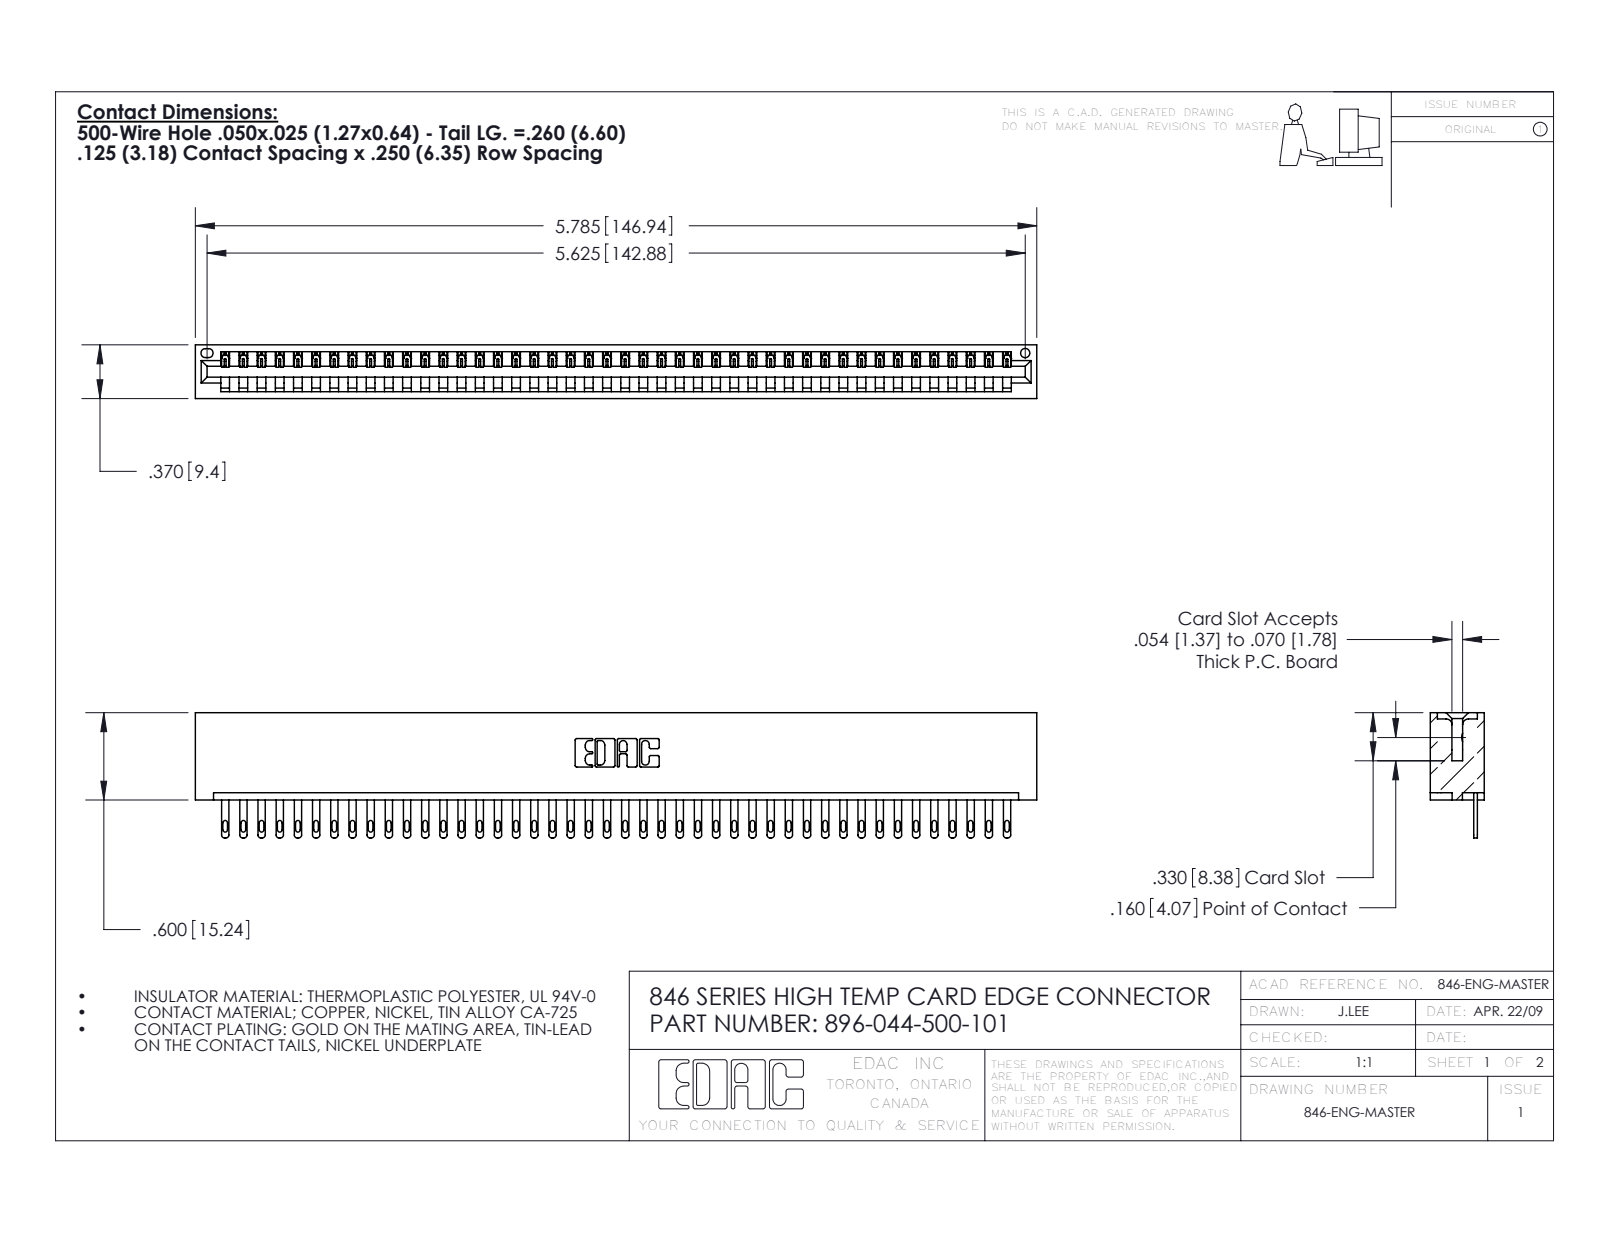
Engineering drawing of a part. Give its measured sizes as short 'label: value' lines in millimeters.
name: 896-044-500-101; 345-292-001_345-293-100; 846 Part_No Mounting Lugs
written by: SolidWorks 2020 (CONFIG_CONTROL_DESIGN)
unit: mm
bodies: 45 solids, 2490 faces (1568 planar, 922 cylindrical, 0 other)
size: 146.9 × 21.8 × 9.4
volume: 14 700 mm³; area: 18 520 mm²
holes: 1× ⌀1.6
rounds: 88× R0.2, 88× R0.4, 88× R0.5, 22× R0.3, 6× R0.2, 6× R0.8, 3× R0.7, 2× R0.8
face distances: 1.2, 8.2, 9.4, 6.4, 1.8, 7.6, 0.6, 3.8, 5.6, 2.5
